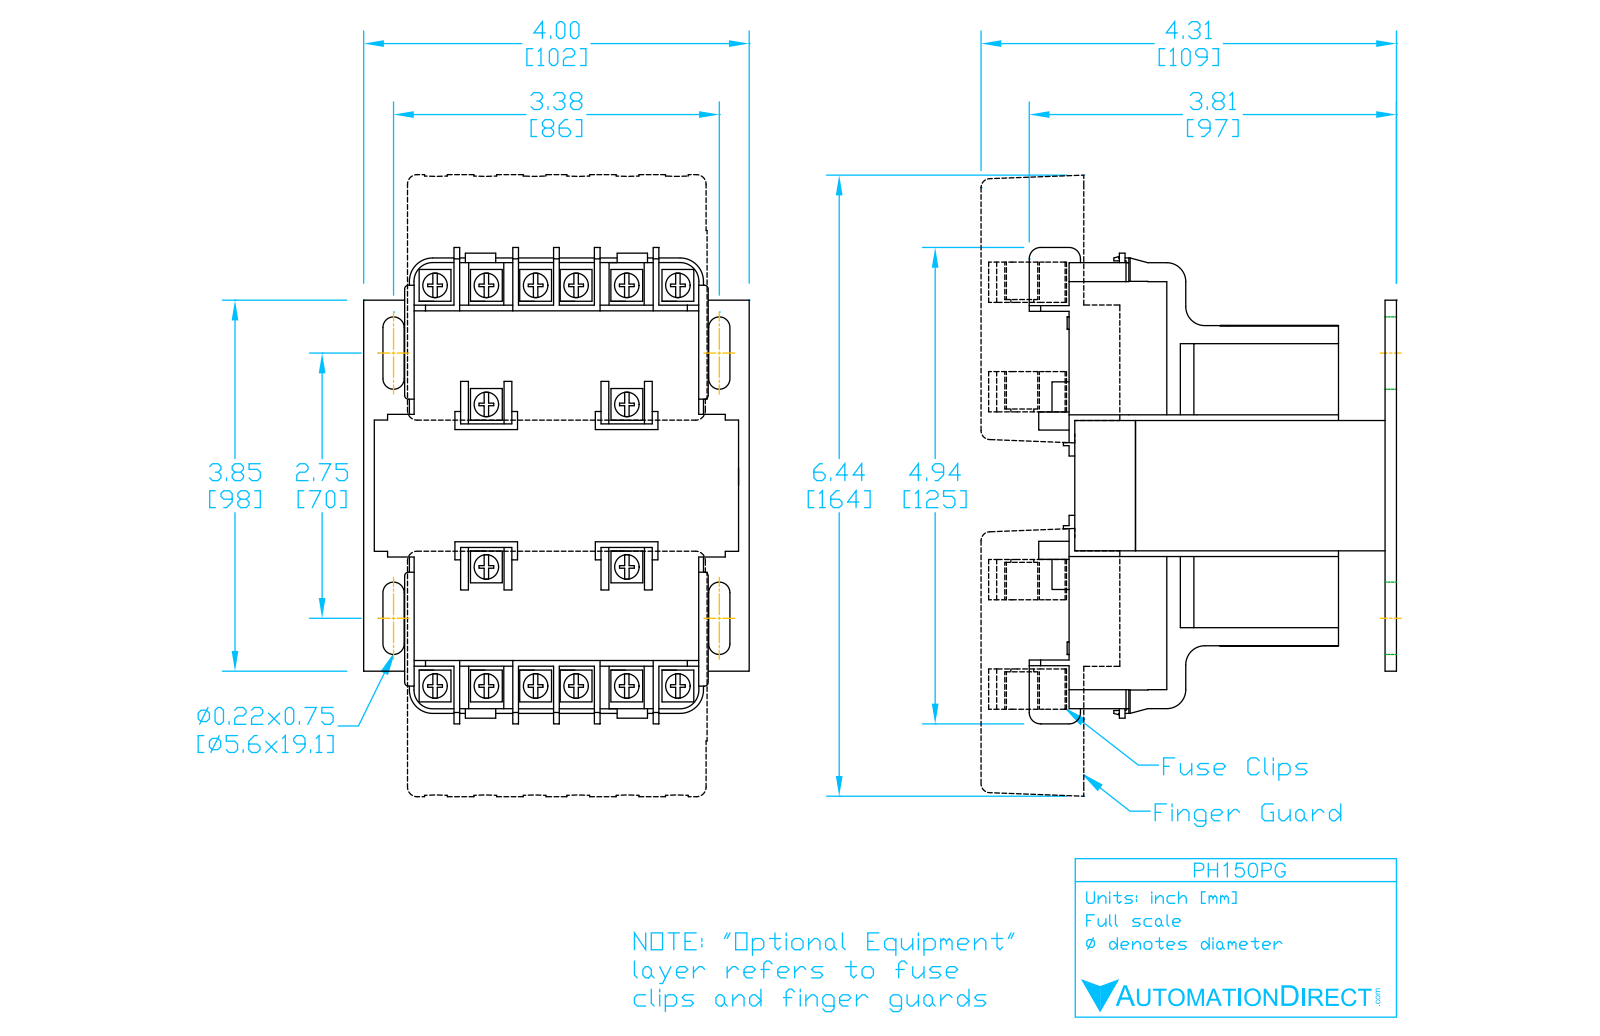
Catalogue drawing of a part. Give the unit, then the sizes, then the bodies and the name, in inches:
Units: inches
Overall size (bounding box): 4.839 × 4 × 3.74
Round holes (diameter × count): ⌀0.157 ×4
Partial cylindrical surfaces — rounded edges, fillets, slot ends (radius × count): R0.039 ×62, R0.197 ×16, R0.11 ×8, R0.1 ×4, R0.188 ×4, R0.243 ×4, R0.472 ×2
Main face-to-face distances: 1.26, 1.033, 0.069, 1.102, 0.118, 2.52, 2.589, 3.622, 0.413, 0.63
Hole centre spacings: 0.787, 3.375, 3.465
Volume: 40.26 in³ · Surface area: 169.8 in²
Bodies: 8 solids, 592 faces (376 planar, 158 cylindrical, 58 other)
Part name (STEP PRODUCT): PH150PG
STEP written by: SolidWorks 2017 (AUTOMOTIVE_DESIGN)
